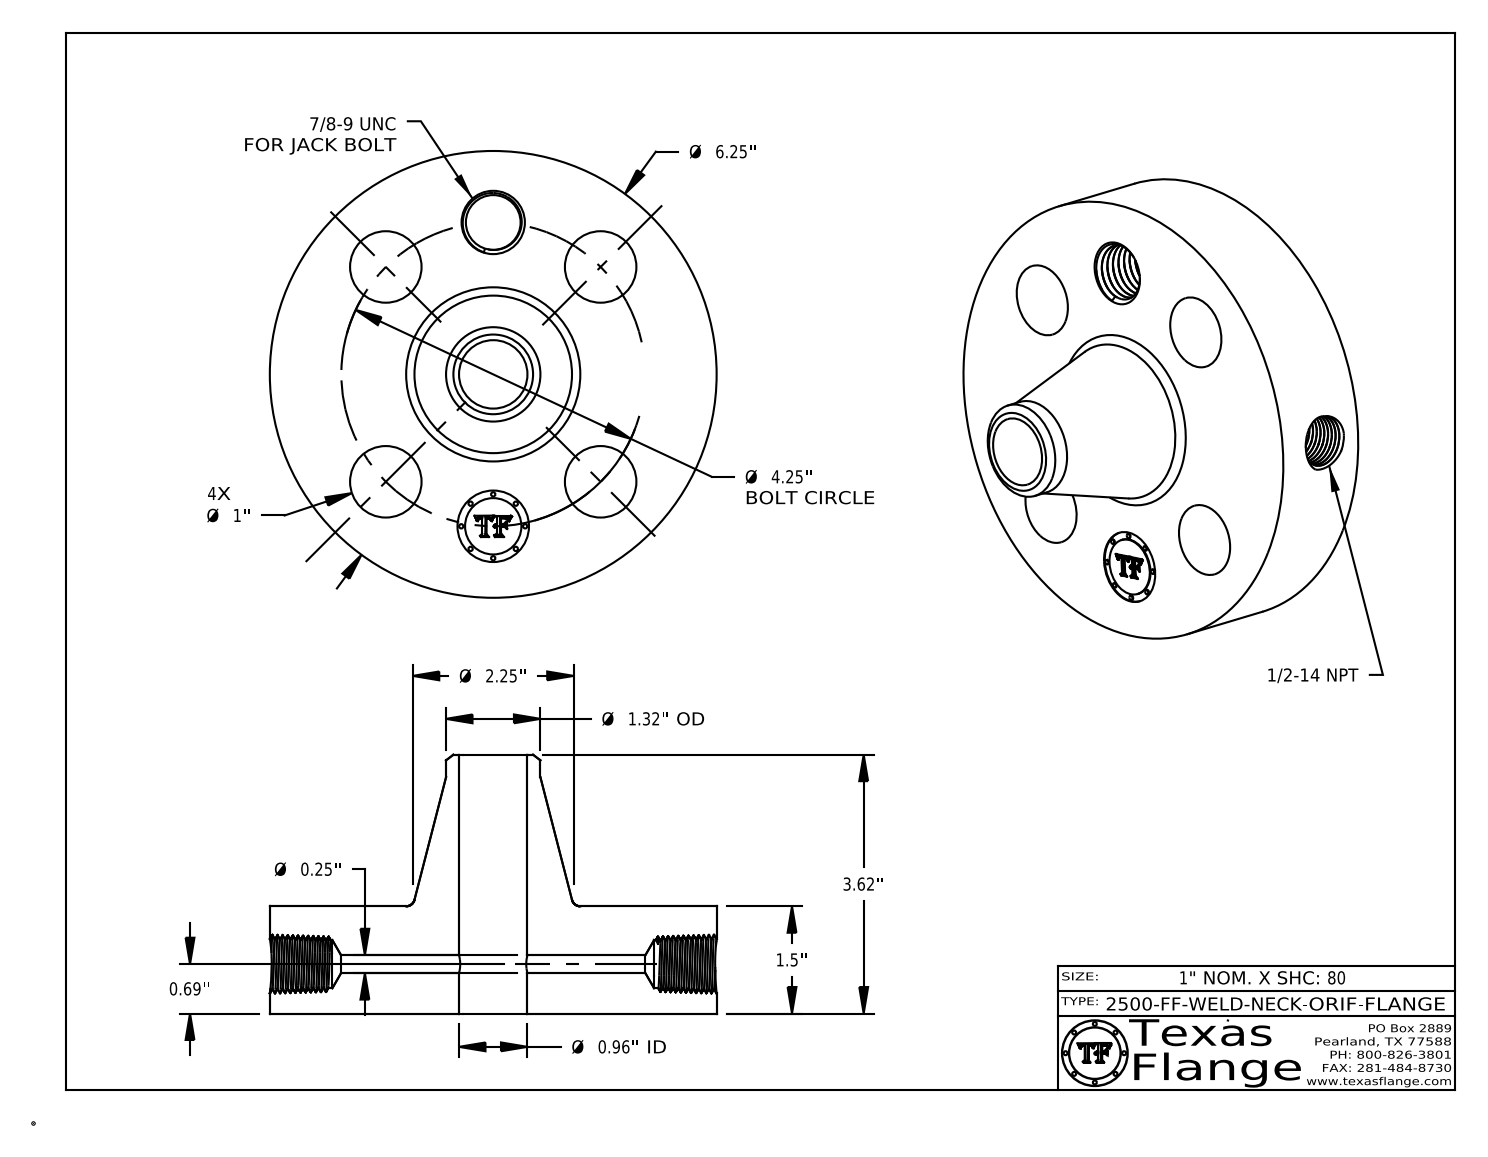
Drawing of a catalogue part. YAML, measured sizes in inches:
part_name: "2500-FF-WELD-NECK"
step_written_by: "CATIA V5 STEP AP214 (AUTOMOTIVE_DESIGN)"
units: inches
bodies: {solids: 1, faces: 748, planar: 368, cylindrical: 80, other: 300}
overall_size: [6.25, 6.25, 3.62]
volume: 42.01
surface_area: 135.5
round_holes:
  - {diameter: 1, count: 5}
  - {diameter: 0.25, count: 1}
  - {diameter: 0.672, count: 1}
  - {diameter: 0.766, count: 1}
  - {diameter: 0.957, count: 1}
round_bosses_or_shafts:
  - {diameter: 0.061, count: 8}
  - {diameter: 6.25, count: 1}
  - {diameter: 1.32, count: 1}
  - {diameter: 0.788, count: 1}
face_to_face_distances: [1.5, 0.015, 1.485, 3.62, 2.135, 2.12, 0.298, 0.292, 0.054, 0.248]
hole_center_spacings: [2.125, 1.626, 3.006, 3.927, 4.25]
